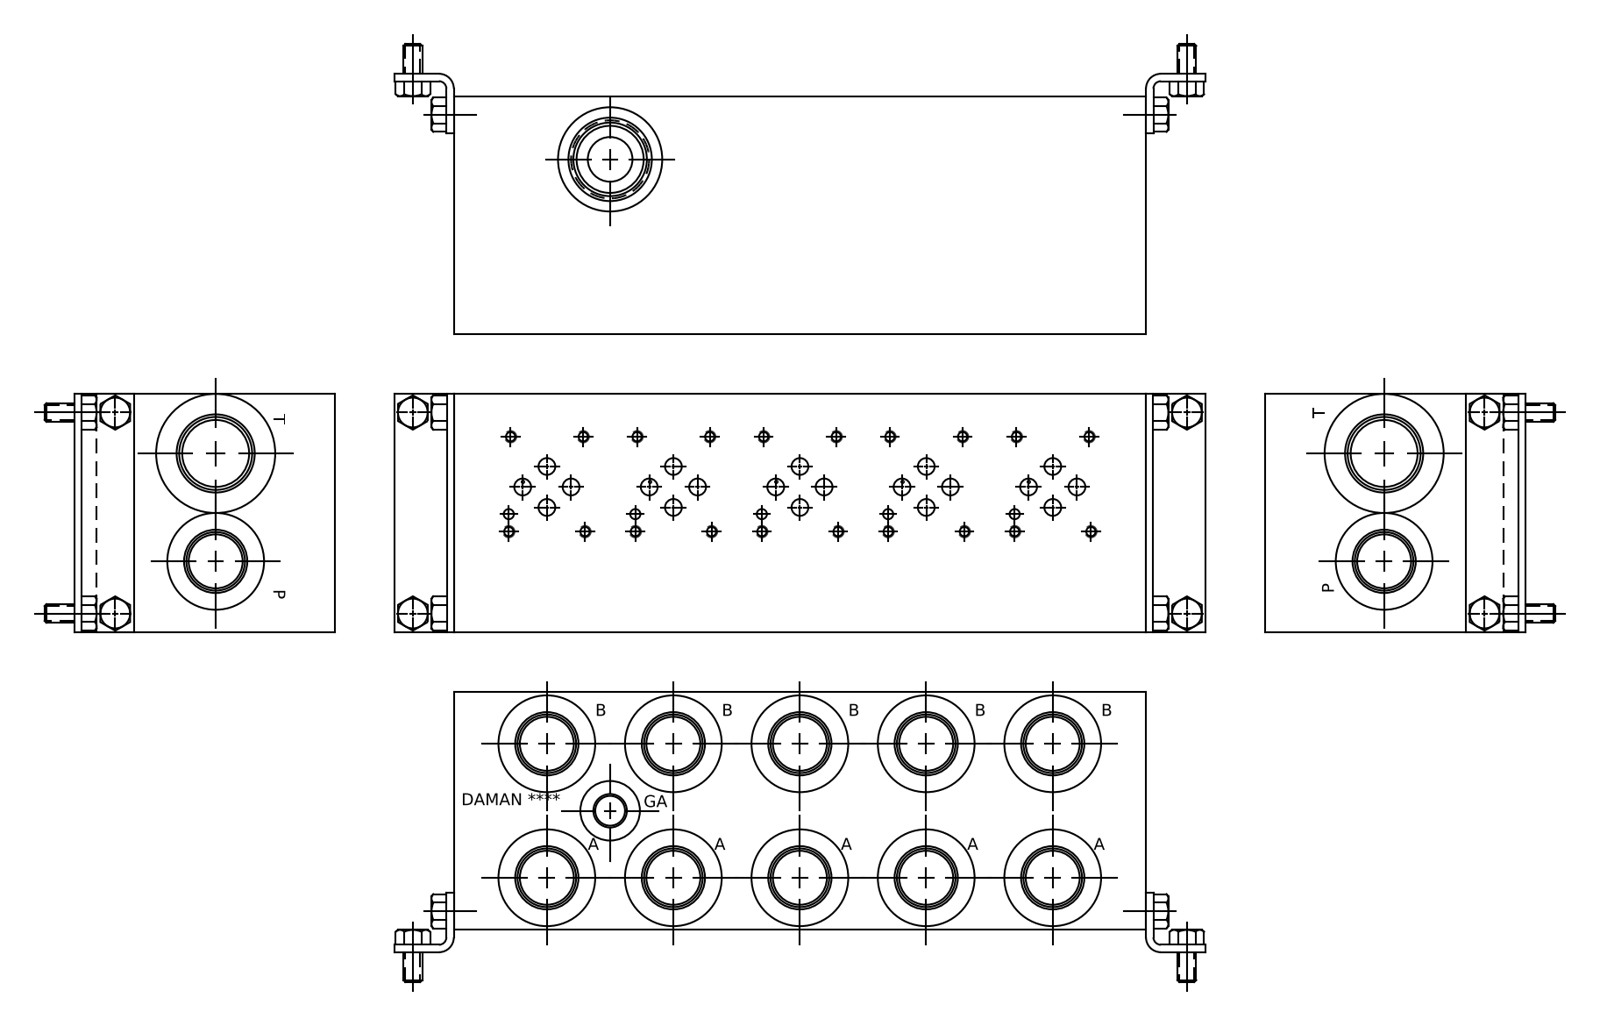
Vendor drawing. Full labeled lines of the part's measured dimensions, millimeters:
Part name (STEP PRODUCT): C:\\Program Files\\PARO\\Hydroman 800\\Export\\AD03HP052S_C_3D
STEP written by: Autodesk Inventor 2012 (AUTOMOTIVE_DESIGN)
Units: millimetres
Bodies: 1 solid, 322 faces (77 planar, 158 cylindrical, 87 other)
Overall size (bounding box): 295.27 × 101.6 × 101.6
Volume: 2 621 000 mm³ · Surface area: 211 741 mm²
Round holes (diameter × count): ⌀3.78 ×20, ⌀4.83 ×20, ⌀7.14 ×20, ⌀24.92 ×11, ⌀29.21 ×11, ⌀41.45 ×11, ⌀23.01 ×10, ⌀27 ×8, ⌀10.72 ×6, ⌀3.96 ×5, ⌀26.99 ×3, ⌀6.53 ×2
Main face-to-face distances: 101.6, 0.76, 295.27, 100.84, 294.51, 293.75, 15.75, 4.09, 3.33, 19.84
Hole centre spacings: 107.95, 53.98, 53.97, 78.61, 40.5, 51.45, 13.52, 13.54
